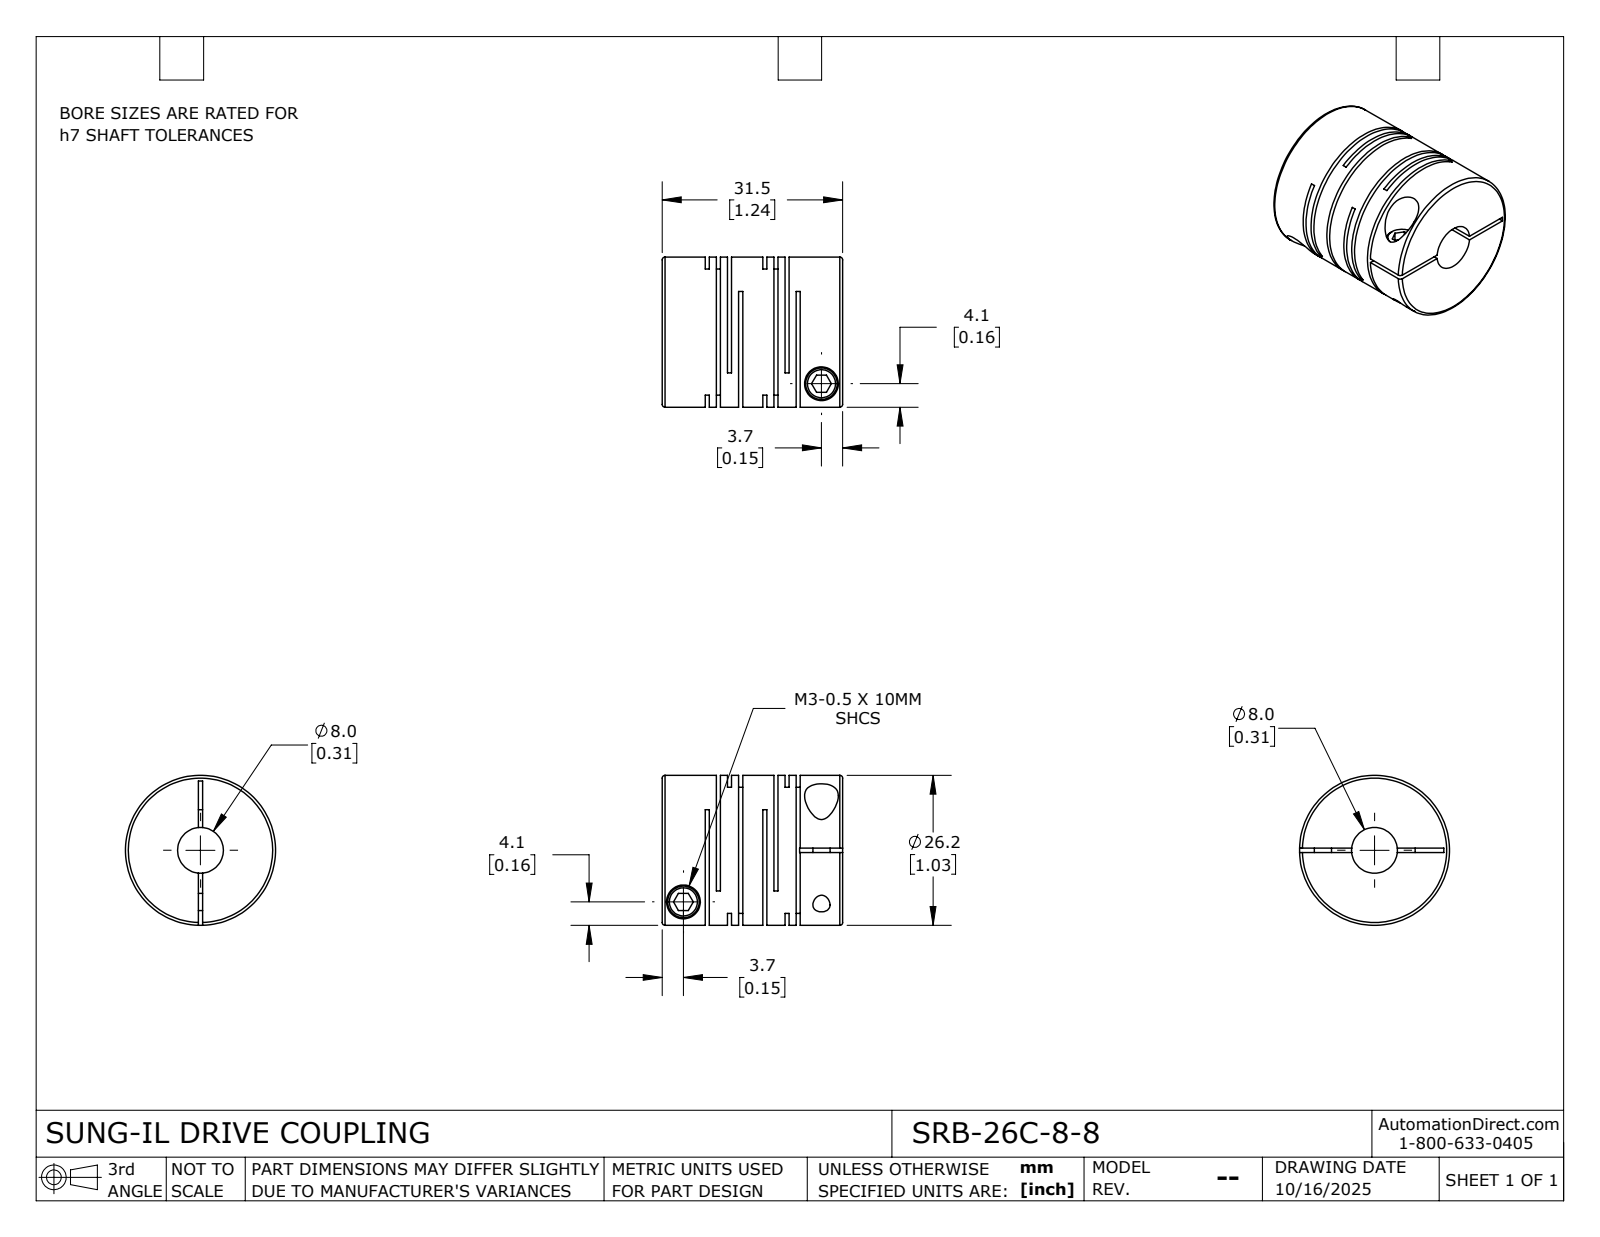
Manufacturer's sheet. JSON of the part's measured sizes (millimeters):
{"part_name": "SRB-26C-8-8", "step_written_by": "SolidWorks 2024 (CONFIG_CONTROL_DESIGN)", "units": "millimeters", "bodies": {"solids": 1, "faces": 115, "planar": 60, "cylindrical": 42, "other": 13}, "overall_size": [31.5, 26.2, 26.2], "volume_mm3": 12649, "surface_area_mm2": 11124, "round_holes": [[3, 2], [5.9, 2], [8, 1]], "round_bosses_or_shafts": [[5.5, 2], [26.2, 1]], "face_to_face_distances": [1.95, 10.05, 0.71, 3.9, 8.1, 12, 1.24, 2.66, 9.34, 13.95]}
